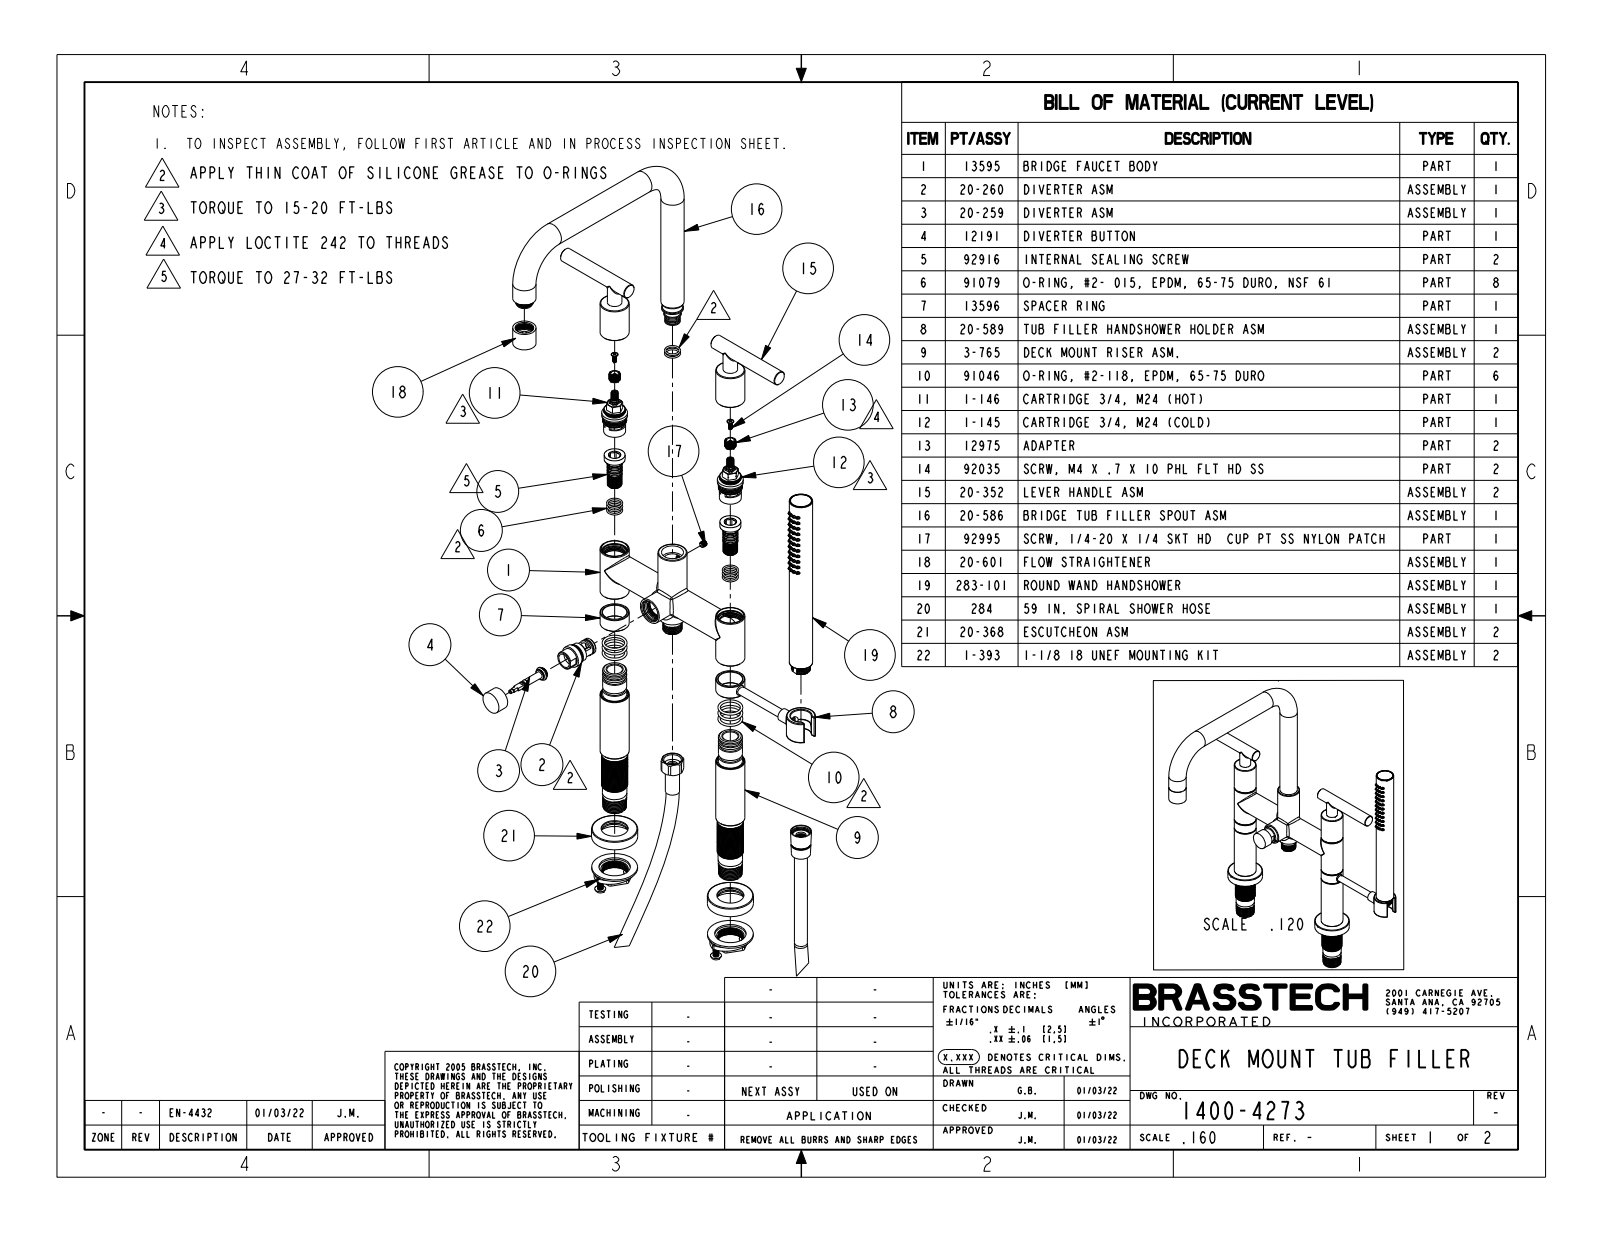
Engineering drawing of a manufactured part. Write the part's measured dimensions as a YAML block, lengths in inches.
part_name: "1400-4273"
step_written_by: "CREO PARAMETRIC BY PTC INC, 2019352 (CONFIG_CONTROL_DESIGN)"
units: inches
bodies: {solids: 5, faces: 1176, planar: 123, cylindrical: 309, other: 744}
overall_size: [31.953, 15.332, 10.49]
volume: 70.54
surface_area: 327.7
round_holes:
  - {diameter: 0.14, count: 44}
  - {diameter: 0.205, count: 1}
  - {diameter: 0.691, count: 1}
round_bosses_or_shafts:
  - {diameter: 1.25, count: 5}
  - {diameter: 1, count: 4}
  - {diameter: 0.625, count: 3}
  - {diameter: 0.56, count: 3}
  - {diameter: 1.98, count: 2}
  - {diameter: 1.15, count: 2}
  - {diameter: 0.965, count: 1}
  - {diameter: 0.825, count: 1}
partial_cylinders:
  - {radius: 0.03, count: 6}
  - {radius: 0.41, count: 1}
  - {radius: 0.494, count: 1}
  - {radius: 0.56, count: 1}
face_to_face_distances: [0.425, 7.84, 7.415, 7.838, 7.413, 3.613, 7.848, 7.423, 4.235, 12.735]
hole_center_spacings: [0.336, 0.604, 0.17, 0.887, 1.172, 0.29, 0.447, 0.58]
